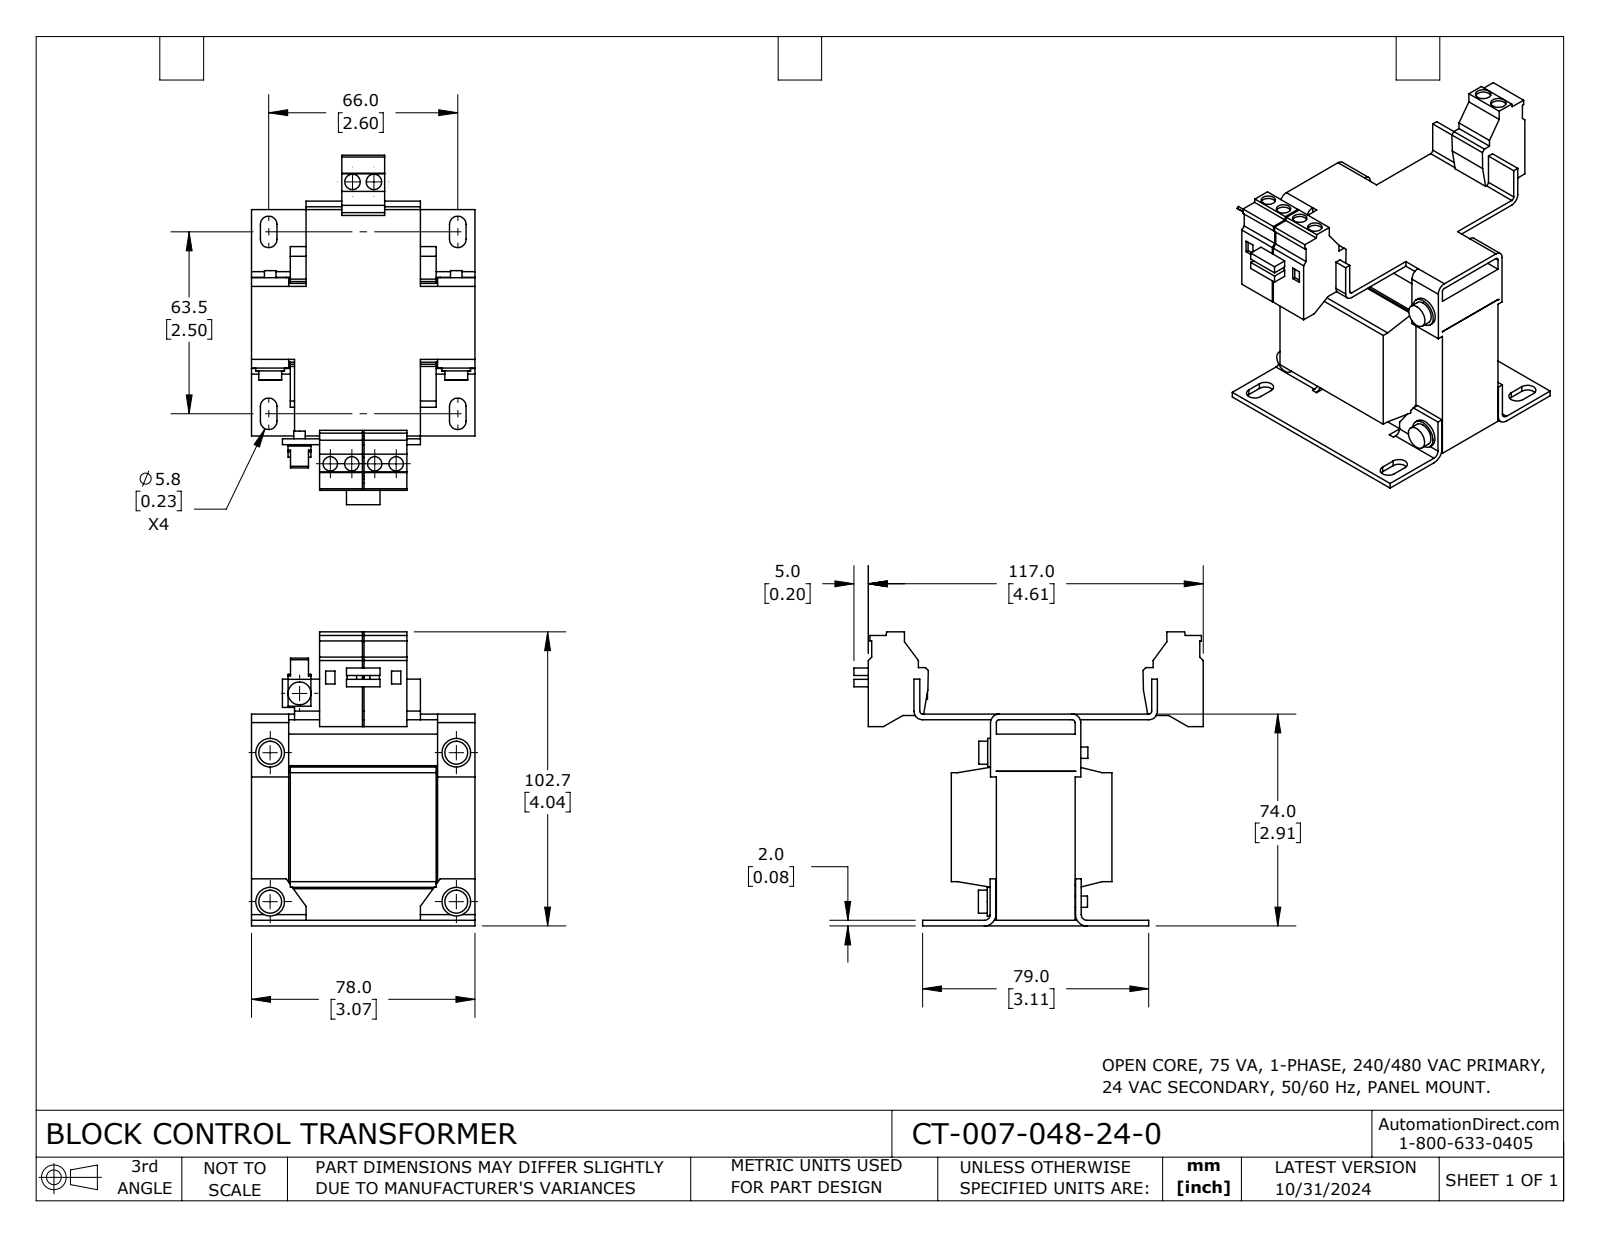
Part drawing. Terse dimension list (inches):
name: CT-007-048-24-0
written by: SolidWorks 2023 (CONFIG_CONTROL_DESIGN)
unit: in
bodies: 1 solid, 375 faces (294 planar, 81 cylindrical, 0 other)
size: 4.803 × 4.043 × 3.071
volume: 14.96 in³; area: 99.05 in²
holes: 4× ⌀0.197, 2× ⌀0.213
bosses: 5× ⌀0.315, 5× ⌀0.157, 4× ⌀0.394, 2× ⌀0.177
rounds: 8× R0.114, 4× R0.039, 4× R0.118, 2× R0.079, 2× R0.157
face distances: 0.079, 2.835, 0.531, 2.047, 0.512, 0.709, 0.02, 2.559, 2.028, 2.756
hole spacings: 3.886, 0.295, 0.61, 3.874, 3.92, 0.315, 0.906
